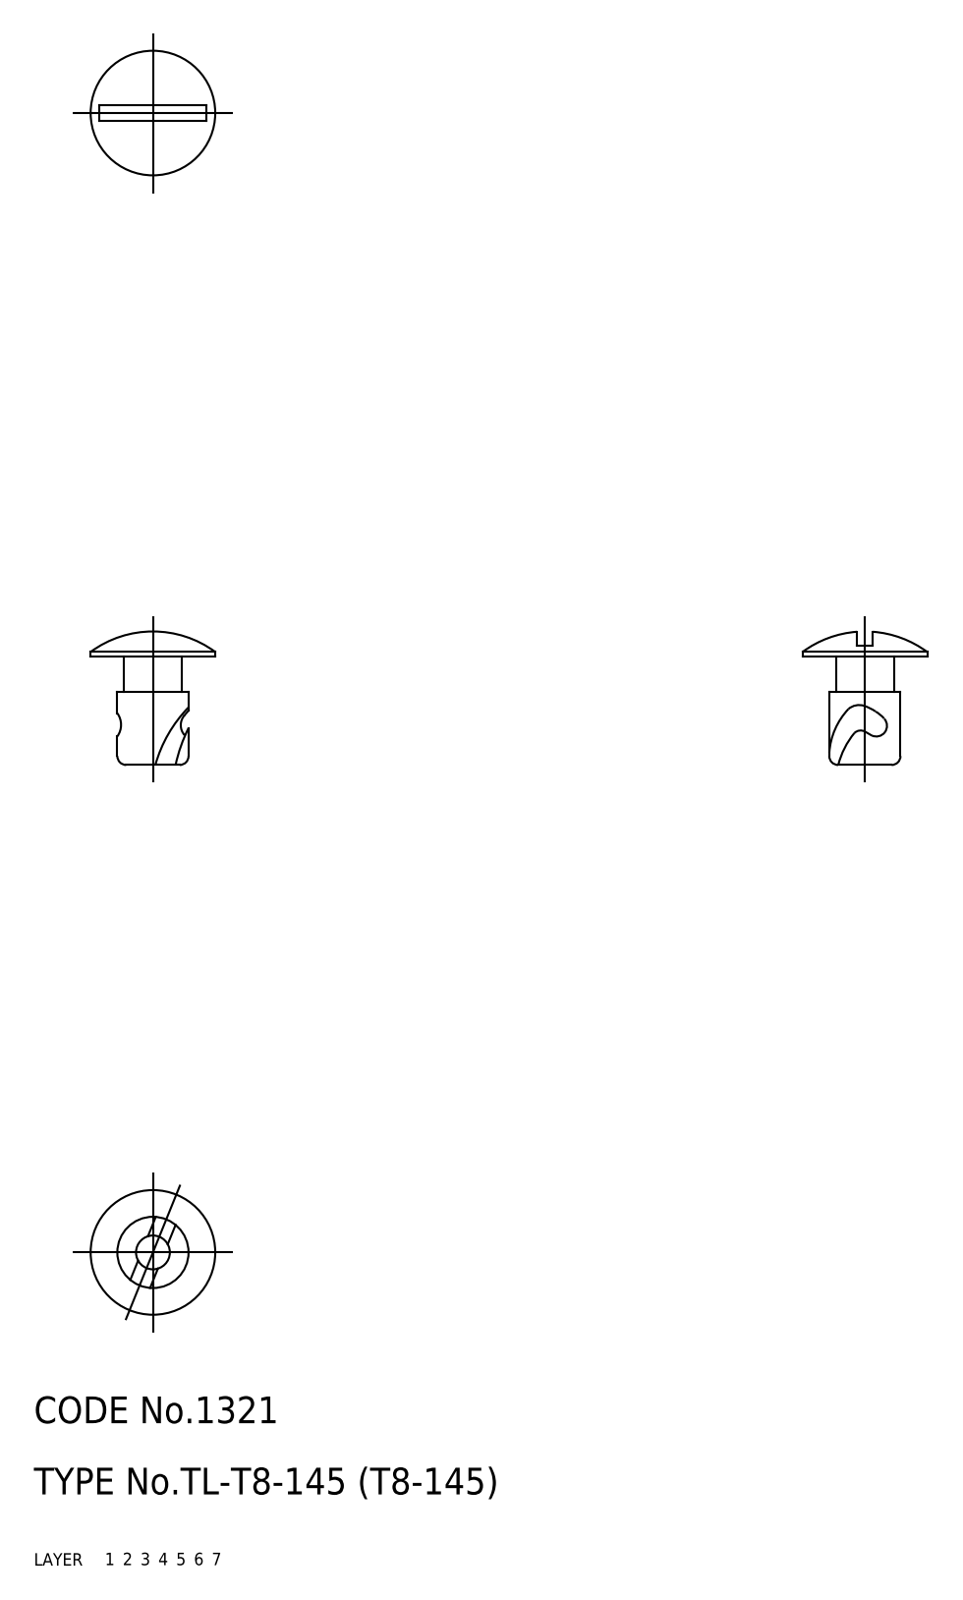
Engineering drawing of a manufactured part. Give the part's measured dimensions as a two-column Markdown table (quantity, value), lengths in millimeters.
| quantity | value |
| --- | --- |
| part name | 67113170 |
| STEP written by | CADfix (AUTOMOTIVE_DESIGN) |
| units | millimeters |
| bodies | 1 solid, 35 faces (0 planar, 0 cylindrical, 35 other) |
| overall size | 14.97 × 14 × 14 |
| volume | 608 mm³ |
| surface area | 765 mm² |
